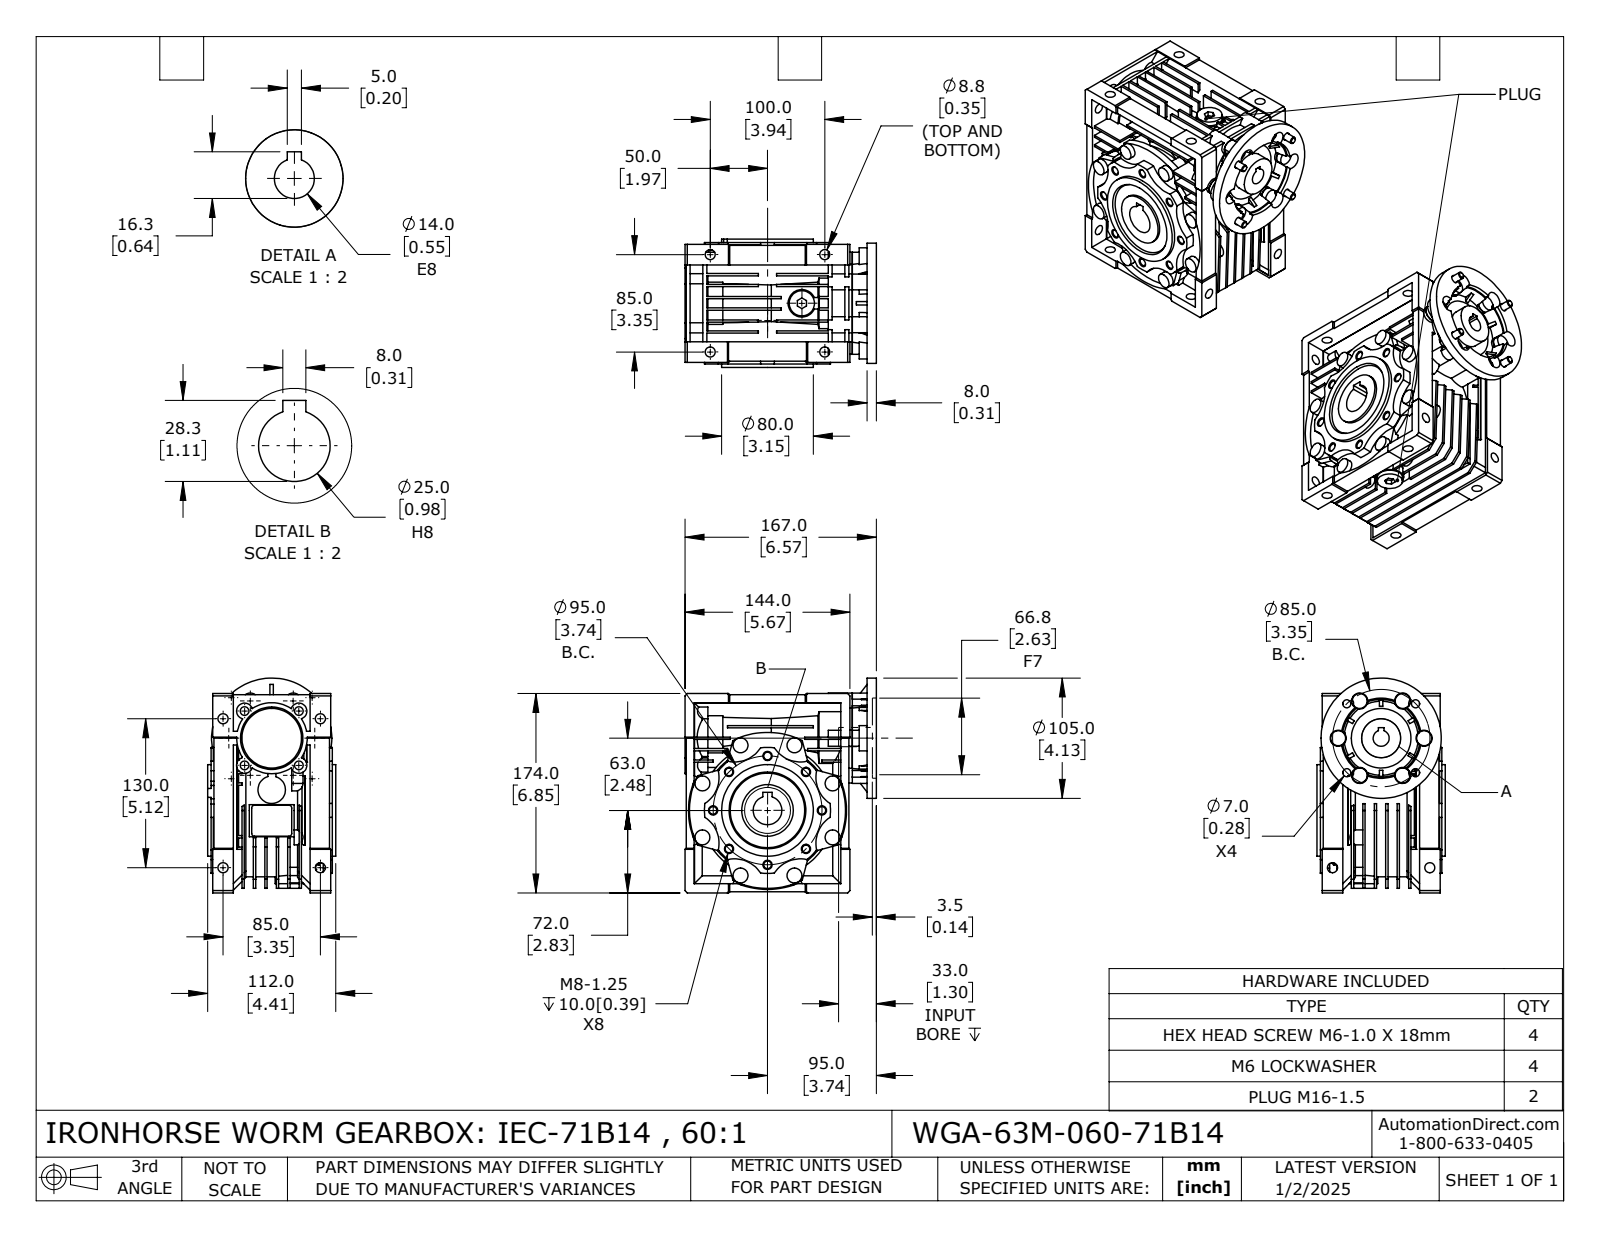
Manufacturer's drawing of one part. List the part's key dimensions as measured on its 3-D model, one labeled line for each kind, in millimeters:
Part name (STEP PRODUCT): WGA-63M-060-71B14
STEP written by: SolidWorks 2024 (CONFIG_CONTROL_DESIGN)
Units: millimetres
Bodies: 16 solids, 1428 faces (836 planar, 417 cylindrical, 175 other)
Overall size (bounding box): 187.5 × 175.5 × 112
Volume: 1 817 000 mm³ · Surface area: 341 752 mm²
Round holes (diameter × count): ⌀6.65 ×8, ⌀8.78 ×8, ⌀6.1 ×4, ⌀7 ×4, ⌀7.56 ×4, ⌀14.5 ×2, ⌀14 ×1, ⌀15 ×1, ⌀25 ×1, ⌀34 ×1, ⌀37 ×1, ⌀45 ×1
Round bosses / shafts (diameter × count): ⌀13 ×14, ⌀14 ×4, ⌀12.2 ×4, ⌀6 ×4, ⌀24 ×3, ⌀22 ×2, ⌀15.8 ×2, ⌀13.7 ×2
Partial cylindrical surfaces — rounded edges, fillets, slot ends (radius × count): R7 ×12, R27 ×8, R6.98 ×6, R11 ×6, R2.5 ×4, R6 ×4, R8.35 ×1, R29.5 ×1
Main face-to-face distances: 10, 8, 20, 2, 30, 7, 12, 40, 18, 1
Hole centre spacings: 36.36, 47.5, 54.12, 67.18, 87.77, 8.99, 33.5, 42.5
